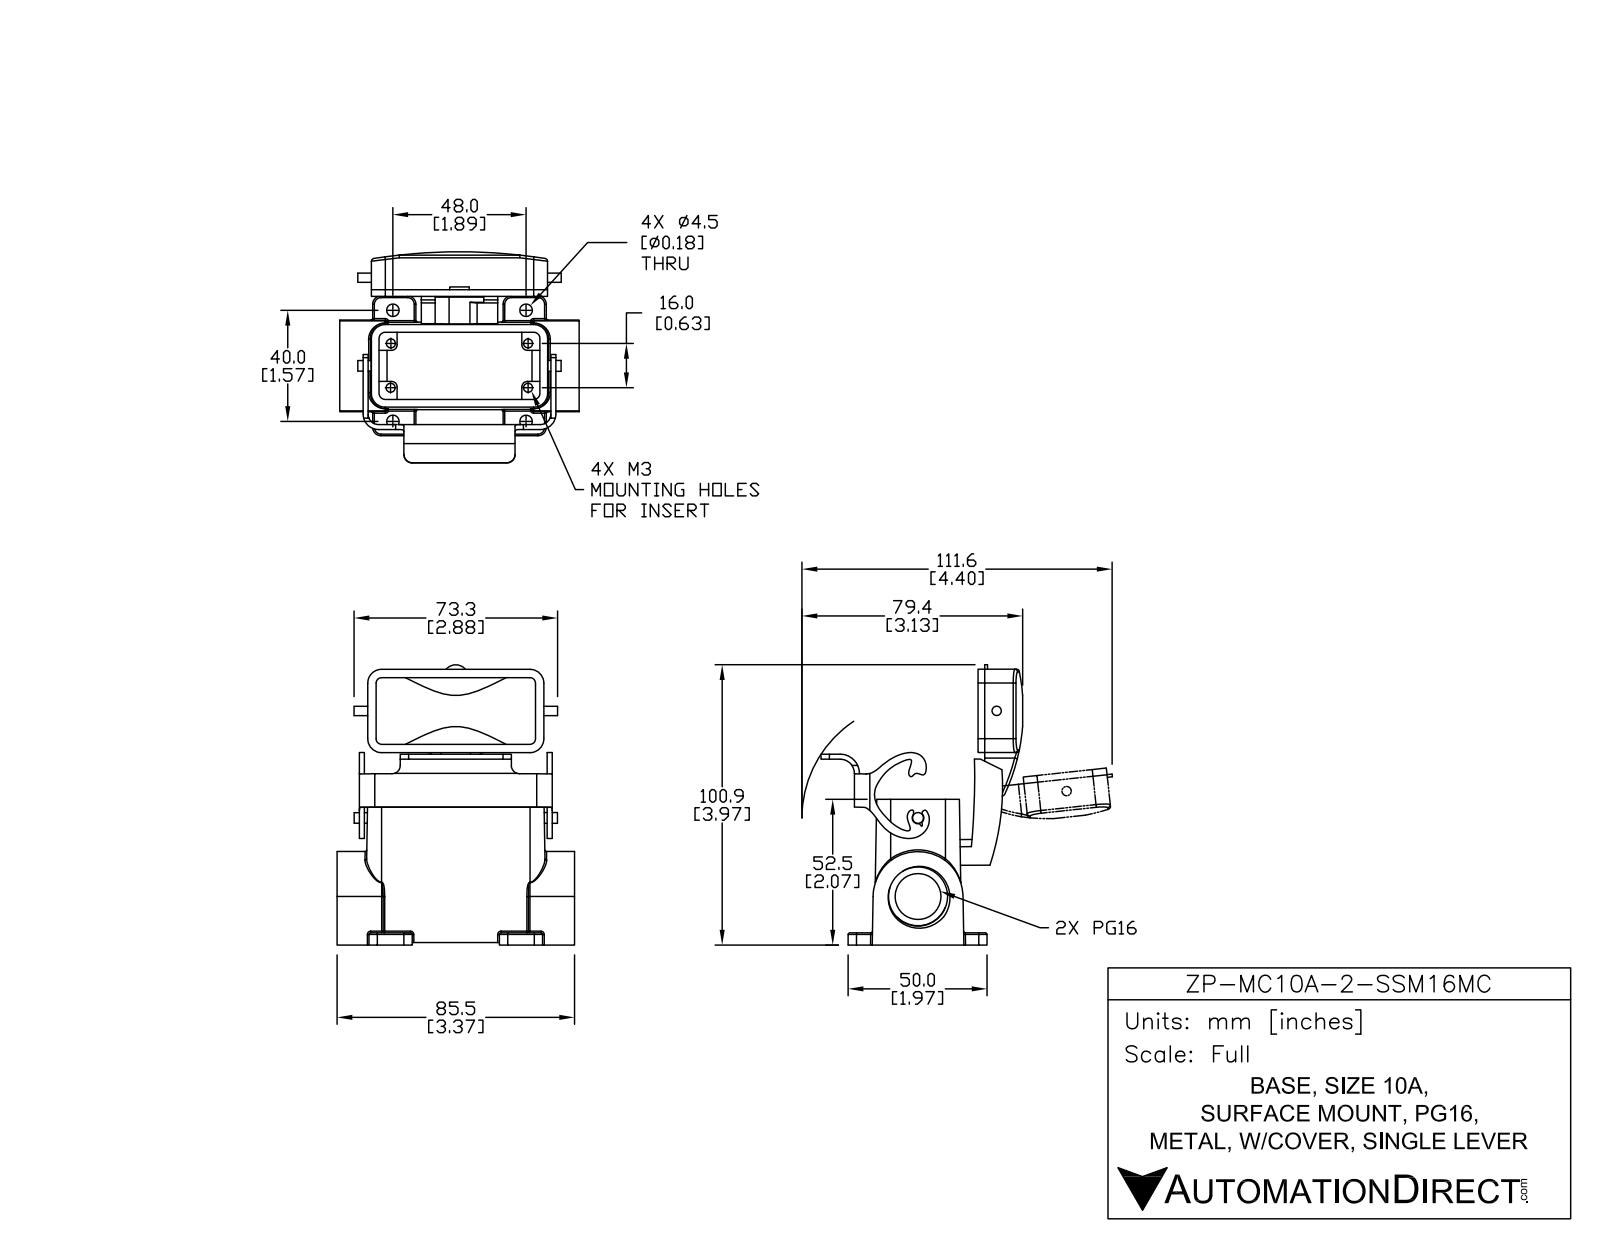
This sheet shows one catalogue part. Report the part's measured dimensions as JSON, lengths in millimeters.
{"part_name": "ZP-MC10A-2-SSM16MC", "step_written_by": "SolidWorks 2014 (AUTOMOTIVE_DESIGN)", "units": "millimeters", "bodies": {"solids": 3, "faces": 408, "planar": 145, "cylindrical": 177, "other": 86}, "overall_size": [100.89, 86.2, 75.98], "volume_mm3": 75798, "surface_area_mm2": 46062, "round_holes": [[3, 4], [4.5, 4], [16.5, 1], [21.25, 1]], "round_bosses_or_shafts": [[7.5, 1], [3.9, 1], [3.8, 1], [3.35, 1]], "partial_cylinders_radius": [[0.6, 28], [3, 12], [2, 10], [5, 6], [1, 5], [3.75, 2], [5.55, 2], [2.1, 1]], "face_to_face_distances": [2.77, 2.78, 3, 4.44, 3.52, 1.8, 27, 0.74, 0.92, 17], "hole_center_spacings": [12.02, 28.01, 50.21, 56.22, 16, 40, 48, 49.5]}
